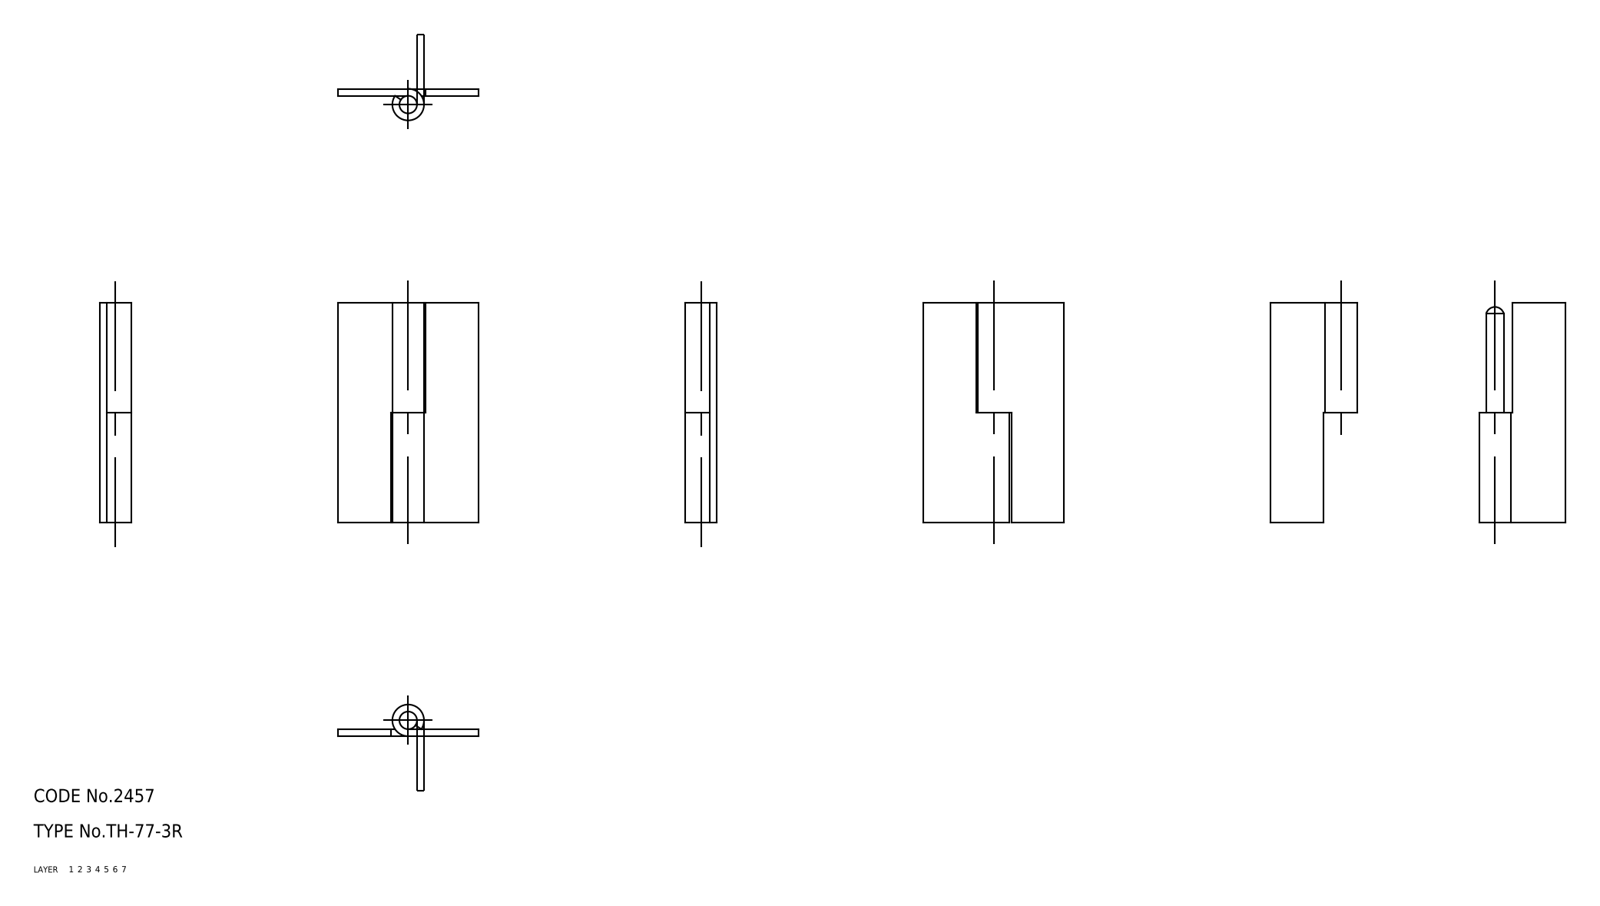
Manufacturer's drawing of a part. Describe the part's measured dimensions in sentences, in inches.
The part is named "shaft; hinge piece_B; hinge piece_A; TH_77_3R_16142_36". Its 3-D file was written by "CADfix (AUTOMOTIVE_DESIGN)". It is 3 solids with 24 faces: 0 planar, 0 cylindrical and 24 other. Overall it measures 1.969 by 1.26 by 0.283 inches. Its volume is 0.246 cubic inches and its surface area 8.41 square inches.
